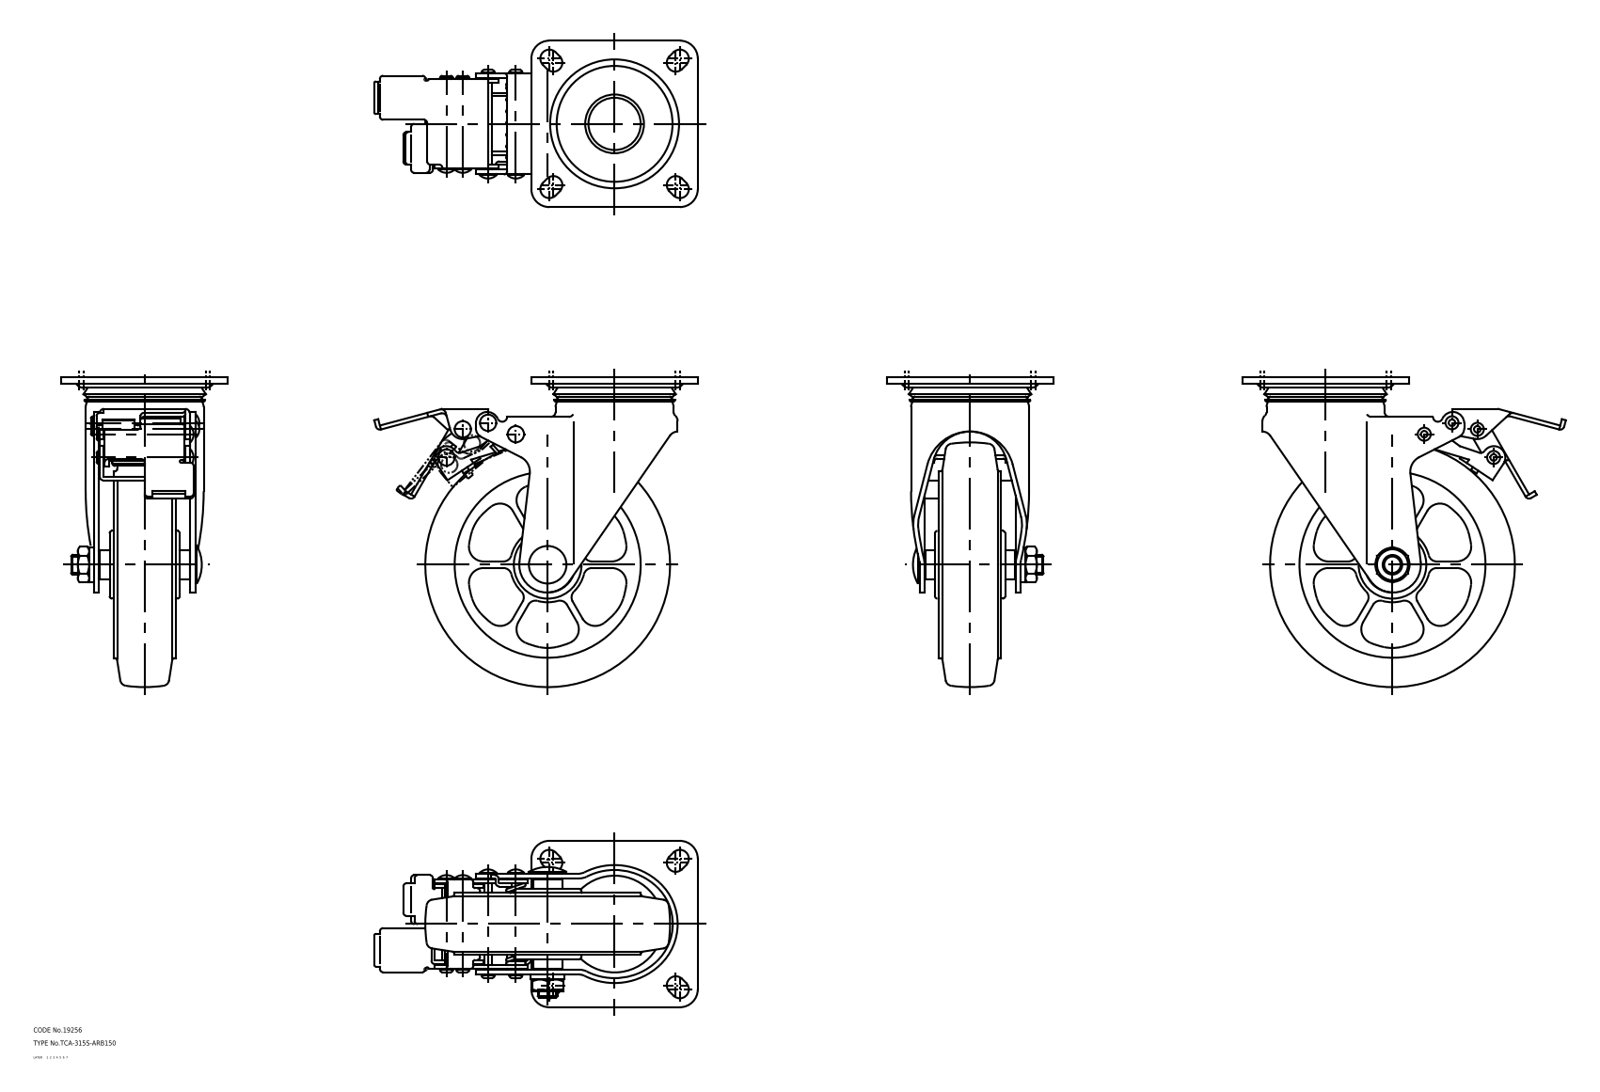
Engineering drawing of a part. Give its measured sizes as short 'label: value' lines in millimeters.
name: lever; wheel; mounting plate; main shaft (+2 more)
written by: CADfix (AUTOMOTIVE_DESIGN)
unit: mm
bodies: 6 solids, 520 faces (0 planar, 0 cylindrical, 520 other)
size: 198.92 × 190 × 102
volume: 623 145 mm³; area: 168 555 mm²
